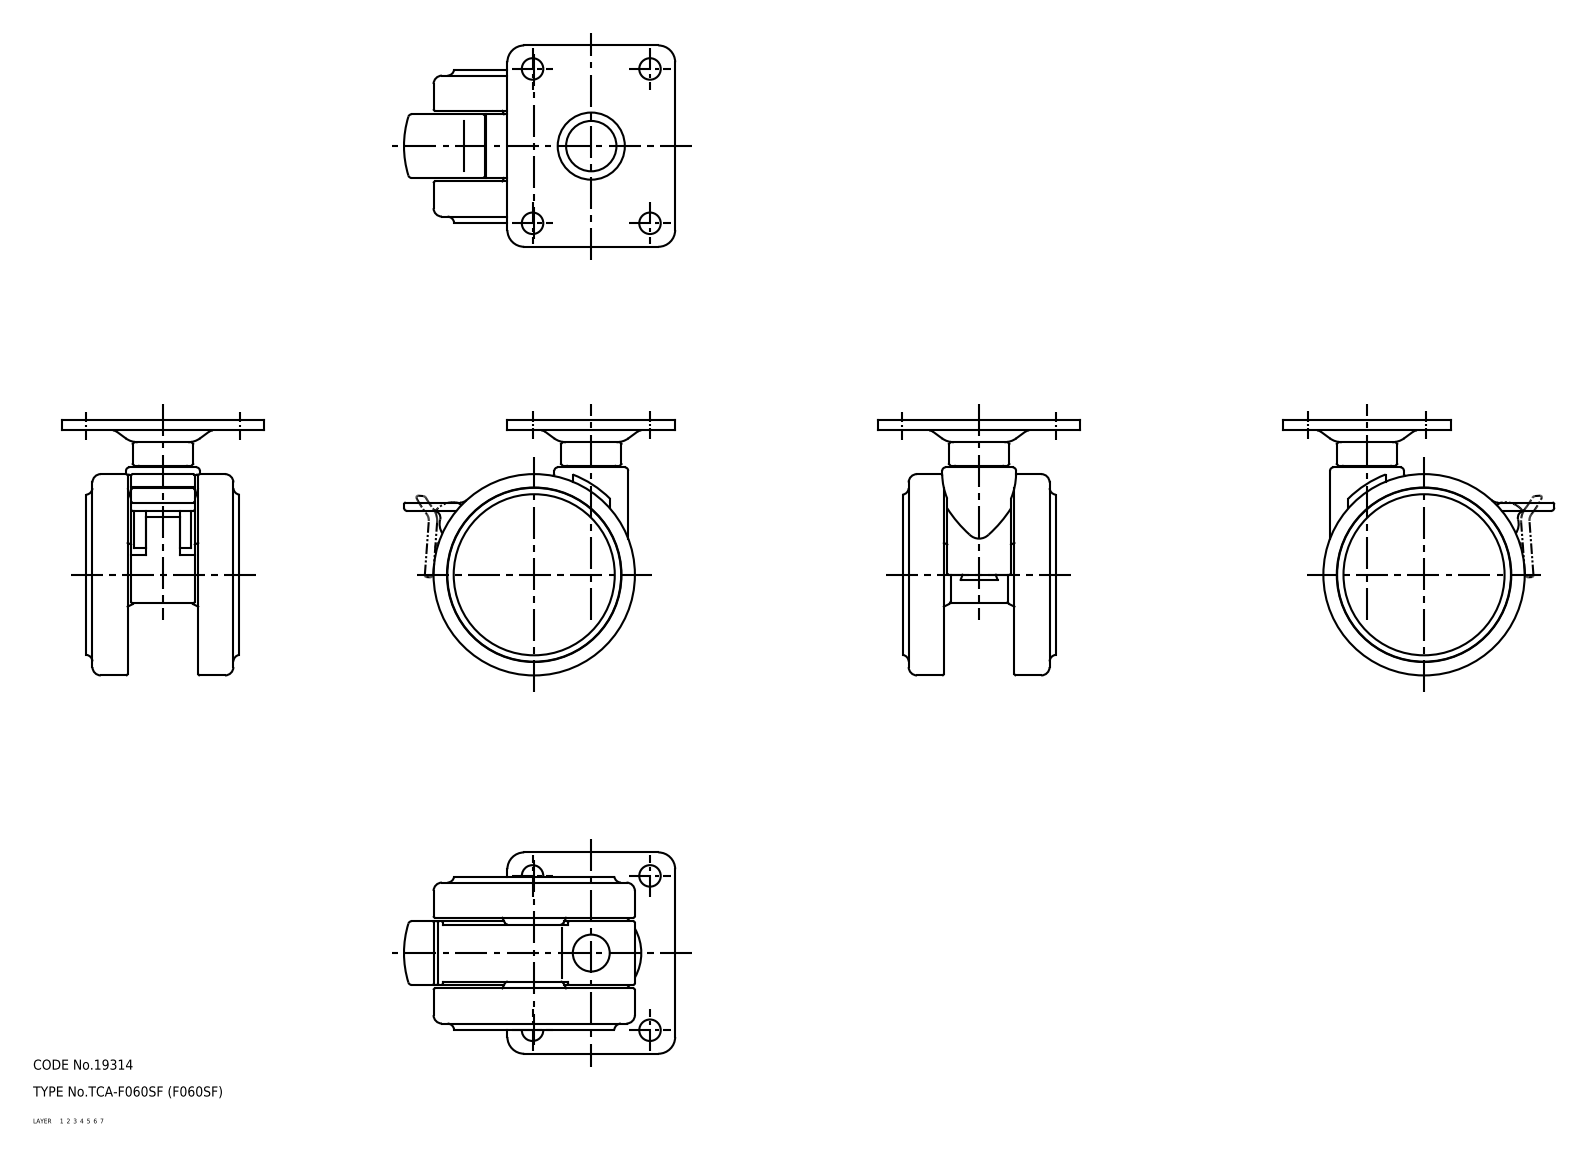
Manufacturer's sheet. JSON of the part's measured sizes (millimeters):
{"part_name": "67126009; 67126022; 67126035; 67126048 (+2 more)", "step_written_by": "CADfix (AUTOMOTIVE_DESIGN)", "units": "millimeters", "bodies": {"solids": 6, "faces": 286, "planar": 0, "cylindrical": 0, "other": 286}, "overall_size": [80.82, 76, 60], "volume_mm3": 91648, "surface_area_mm2": 36593}
